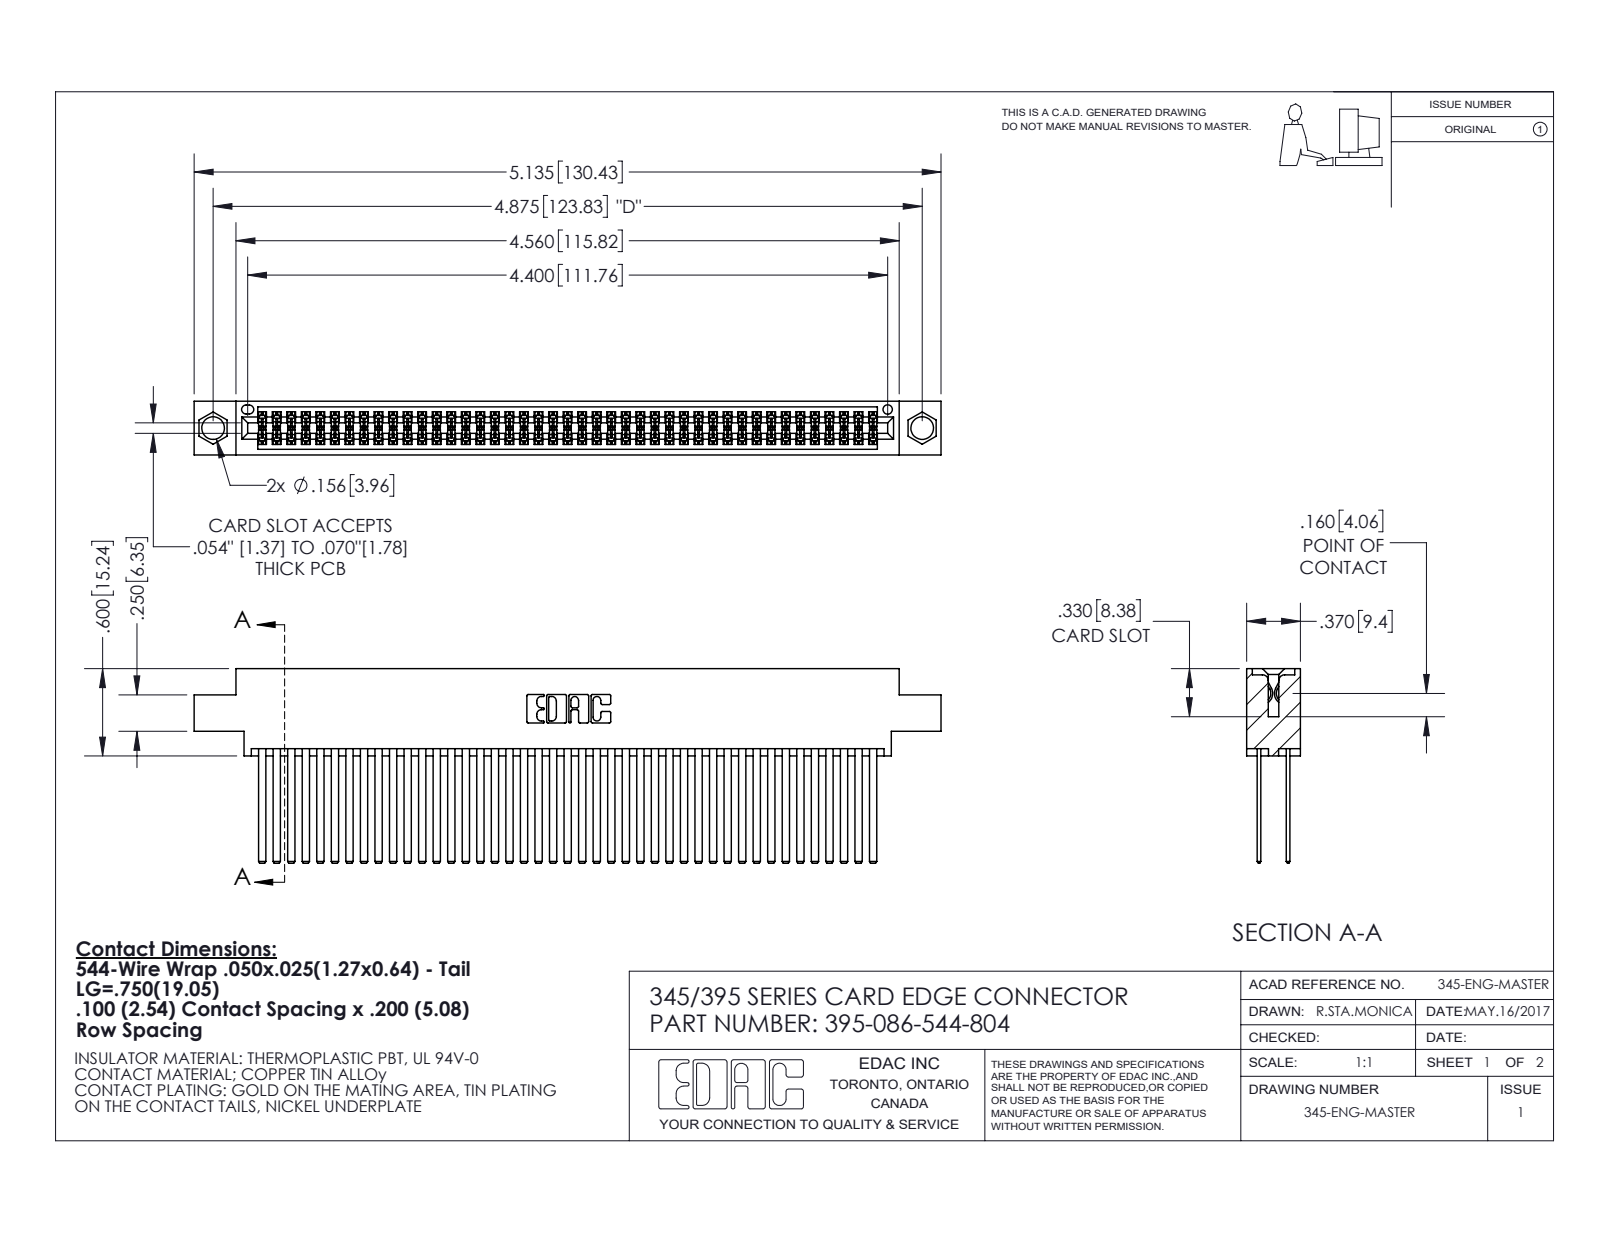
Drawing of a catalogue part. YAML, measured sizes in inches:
part_name: "395-086-544-804; 345 Part_0.170 Offset - 0.156 Dia-TI; 345-292-001_345-293-144"
step_written_by: "SolidWorks 2020 (CONFIG_CONTROL_DESIGN)"
units: inches
bodies: {solids: 87, faces: 3928, planar: 2592, cylindrical: 1336, other: 0}
overall_size: [5.135, 1.337, 0.37]
volume: 0.834
surface_area: 36.81
round_holes:
  - {diameter: 0.156, count: 2}
  - {diameter: 0.064, count: 1}
partial_cylinders:
  - {radius: 0.006, count: 129}
  - {radius: 0.01, count: 22}
  - {radius: 0.007, count: 6}
  - {radius: 0.031, count: 6}
  - {radius: 0.026, count: 3}
  - {radius: 0.014, count: 2}
  - {radius: 0.019, count: 2}
  - {radius: 0.022, count: 2}
face_to_face_distances: [0.2, 0.025, 0.072, 0.098, 0.272, 0.298, 0.225, 0.175, 0.37, 0.15]
hole_center_spacings: [0.27, 4.639, 4.875]
